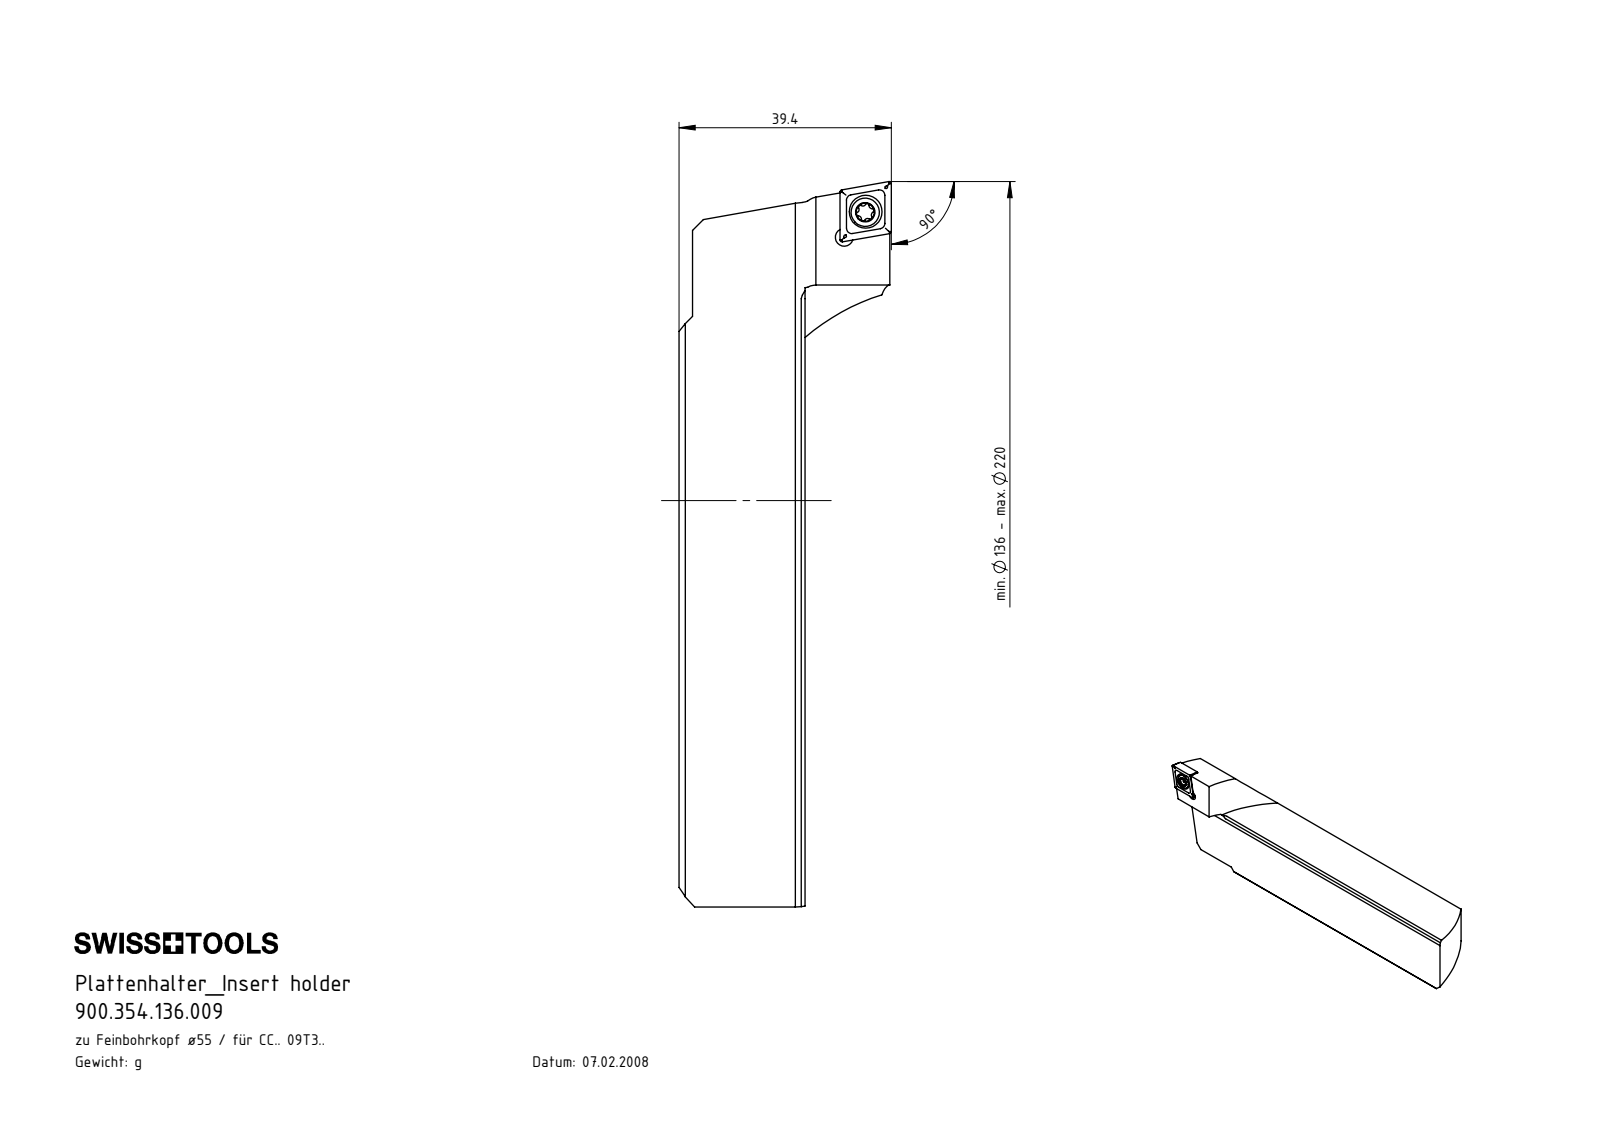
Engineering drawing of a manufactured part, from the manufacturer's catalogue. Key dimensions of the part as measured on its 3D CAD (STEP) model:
Part name (STEP PRODUCT): 900.354.136.009; F00-WCB.136.001_C; CCMT09T304; WCB-ER2.001.009_A
STEP written by: SolidWorks 2017 (CONFIG_CONTROL_DESIGN)
Units: millimetres
Bodies: 3 solids, 559 faces (342 planar, 39 cylindrical, 178 other)
Overall size (bounding box): 134.57 × 39.4 × 27.35
Volume: 55 658 mm³ · Surface area: 14 000 mm²
Round holes (diameter × count): ⌀3.3 ×2, ⌀4.4 ×1, ⌀6.1 ×1
Round bosses / shafts (diameter × count): ⌀5.25 ×1, ⌀4 ×1
Partial cylindrical surfaces — rounded edges, fillets, slot ends (radius × count): R0.2 ×8, R0.34 ×6, R0.59 ×6, R40 ×3, R0.8 ×1
Main face-to-face distances: 2.38, 21.3, 4.76, 7.14, 9.52, 4.77, 7.15, 9.53, 11.91, 14.29
Hole centre spacings: 6.06, 6.19
